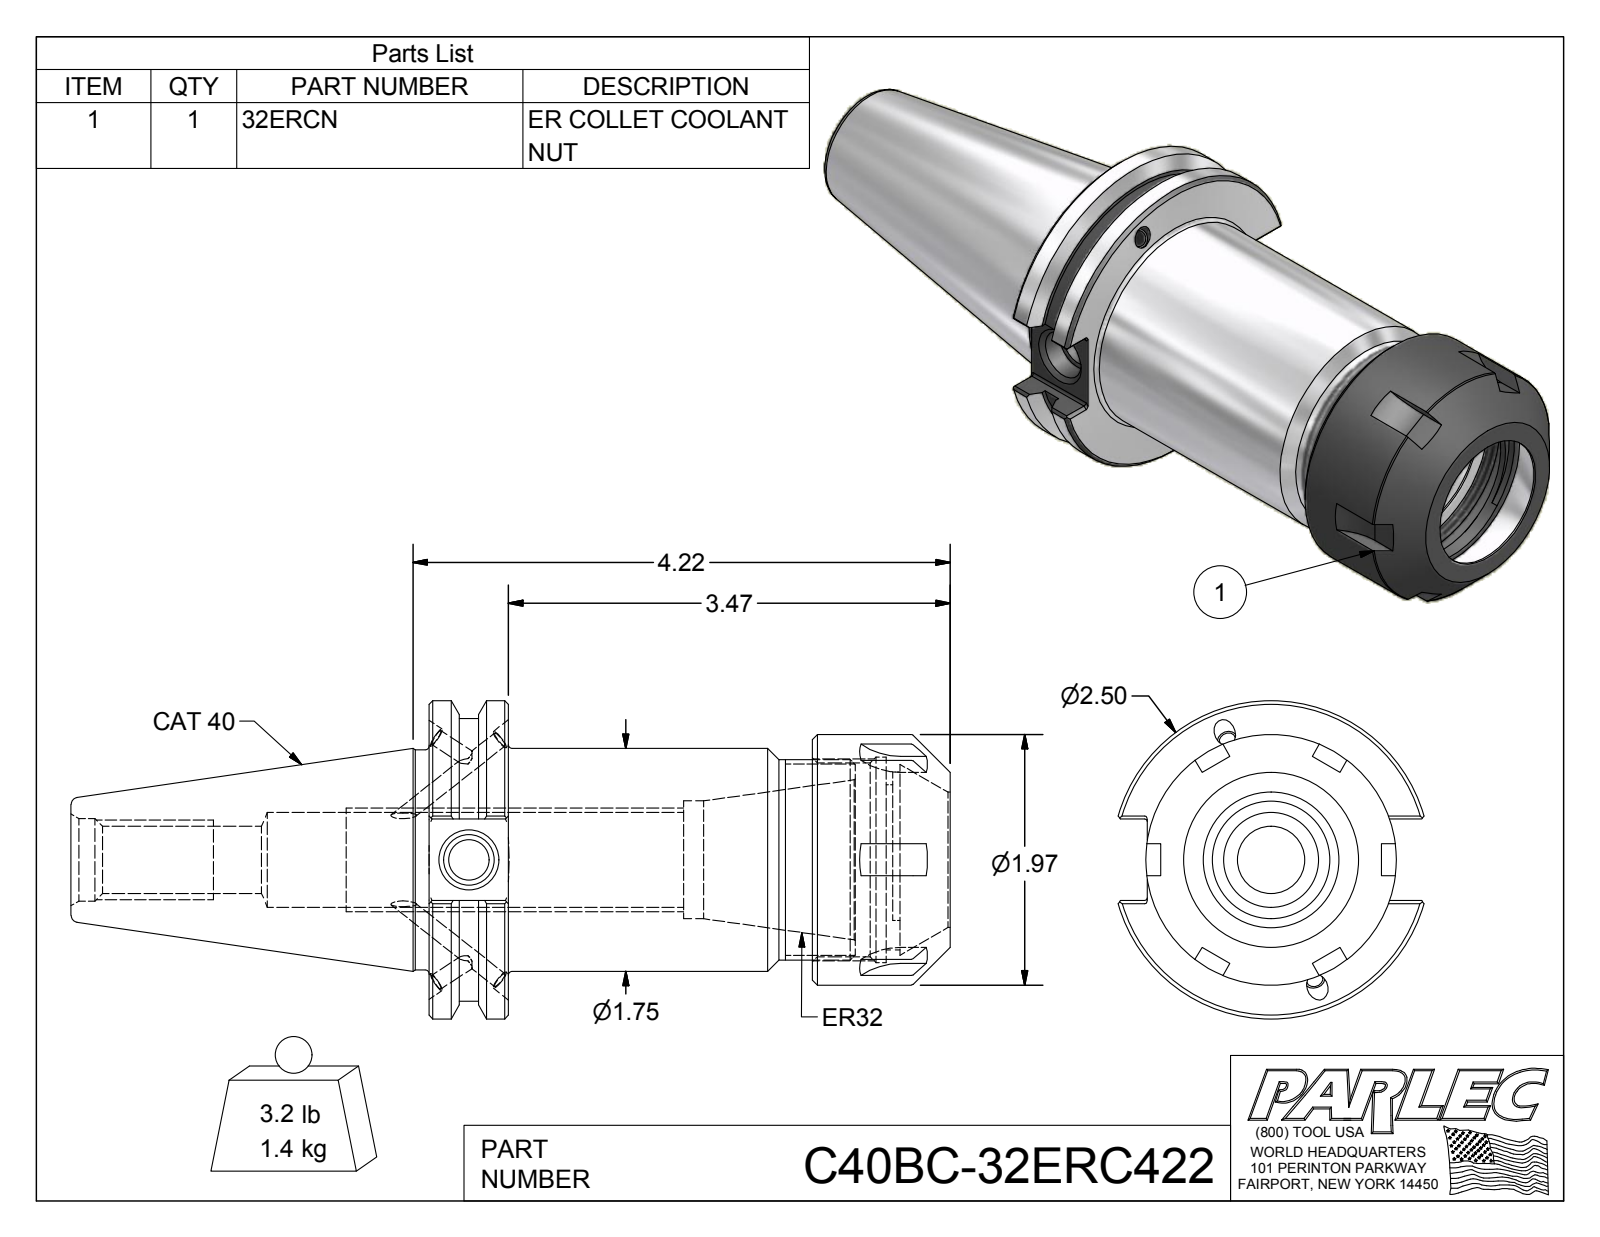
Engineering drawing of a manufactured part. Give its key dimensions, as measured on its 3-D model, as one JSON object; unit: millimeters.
{"part_name": "C40BC-32ERC422; 32ERCN; C40BC-32ER4-1", "step_written_by": "Autodesk Inventor 2012 (AUTOMOTIVE_DESIGN)", "units": "millimeters", "bodies": {"solids": 2, "faces": 143, "planar": 59, "cylindrical": 47, "other": 37}, "overall_size": [175.5, 63.5, 61], "volume_mm3": 185700, "surface_area_mm2": 45410, "round_holes": [[3.3, 4], [4.1, 4], [8, 1], [10.1, 1], [13.4, 1], [16.5, 1], [18.9, 1], [23.5, 1], [27, 1], [33, 1], [38.7, 1], [41, 1]], "round_bosses_or_shafts": [[63.5, 1], [56.4, 1], [50, 1], [44.5, 1], [43.9, 1], [40, 1]], "partial_cylinders_radius": [[0.5, 12], [12.7, 6], [17.5, 1]], "face_to_face_distances": [15.9, 76.5, 60.6, 91.2, 75.3, 14.7, 104, 88.1, 27.5, 12.8], "hole_center_spacings": [1.5]}
